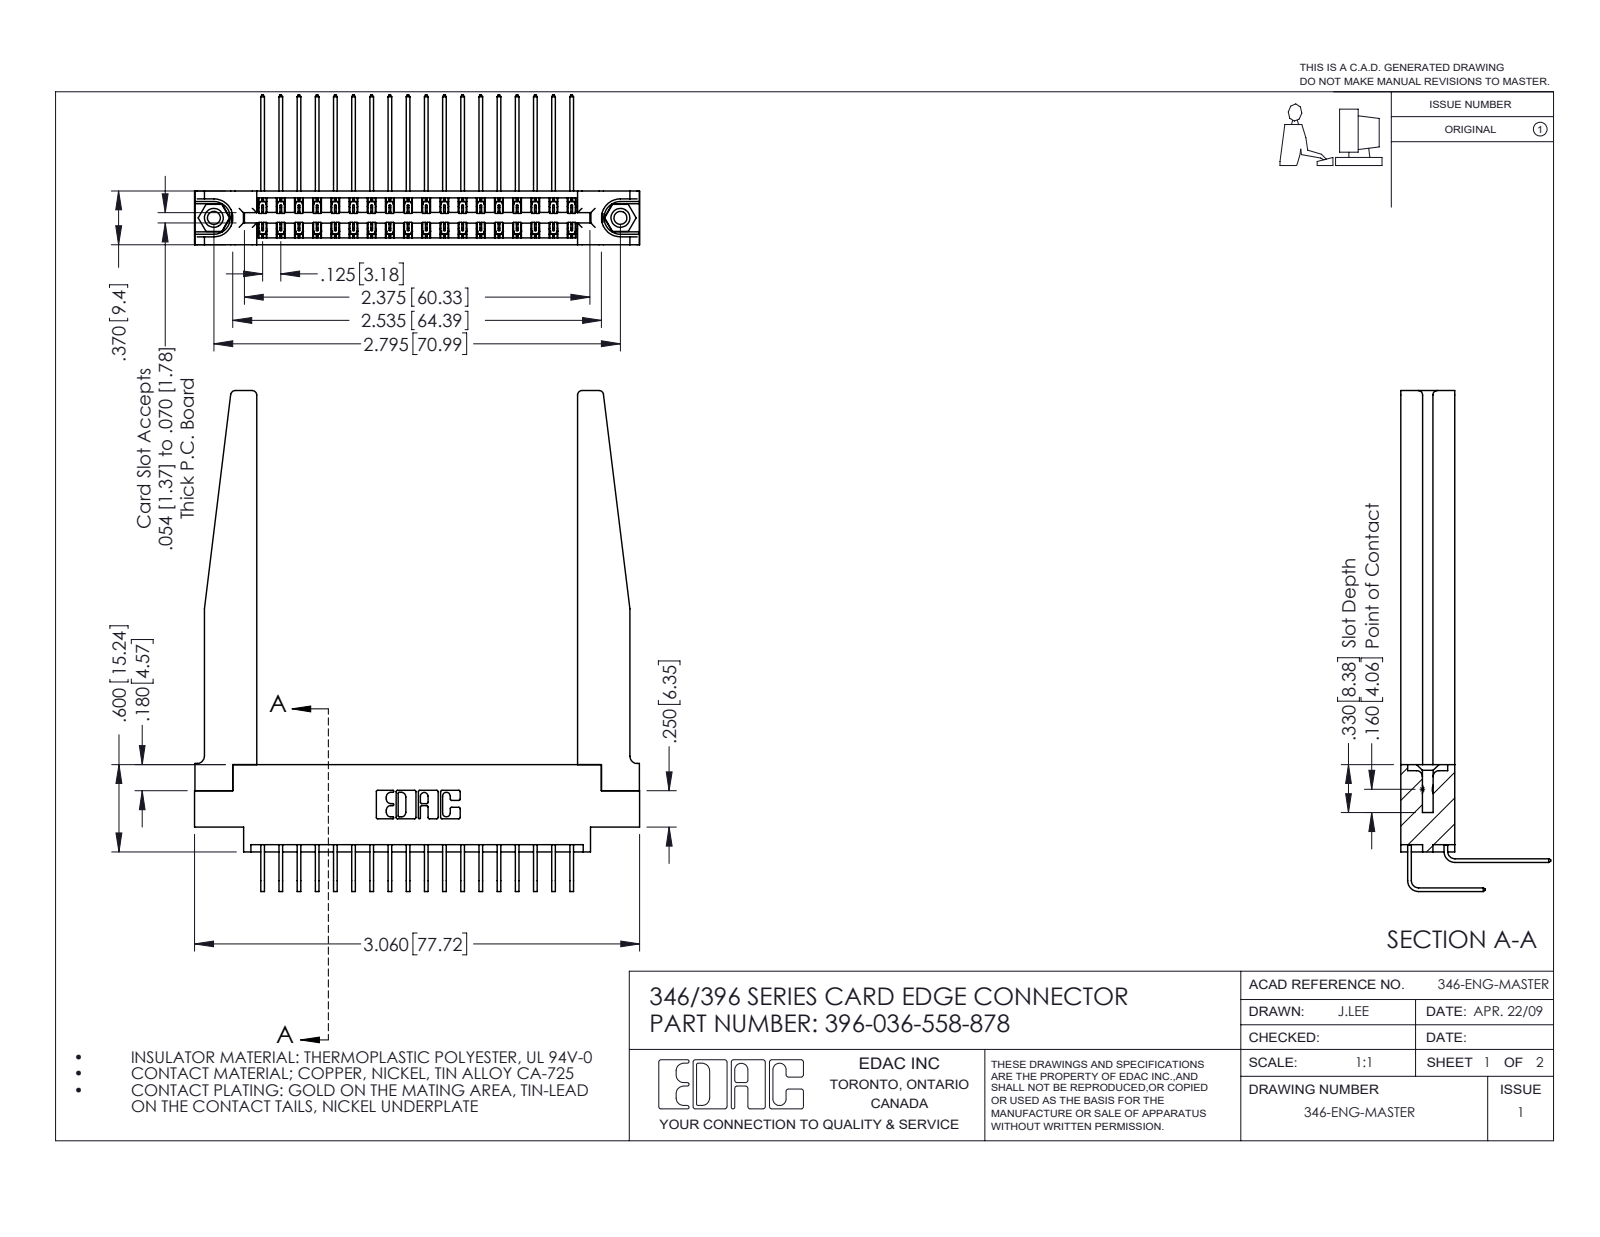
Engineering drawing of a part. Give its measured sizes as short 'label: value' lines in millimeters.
name: 346 Part_0.170 Offset - 0.156 Dia-TH; 345-250-001_345-250-001-102; 345-292-001_558 559 Tail - 1; 346-220-078_345-220-078 (+2 more)
written by: SolidWorks 2016 (CONFIG_CONTROL_DESIGN)
unit: mm
bodies: 41 solids, 2304 faces (1554 planar, 698 cylindrical, 52 other)
size: 87.5 × 77.7 × 26.2
volume: 14 400 mm³; area: 17 570 mm²
holes: 2× ⌀2.3, 2× ⌀3.2, 2× ⌀4, 1× ⌀1.6
bosses: 2× ⌀3.9
rounds: 54× R0.2, 22× R0.3, 8× R0.8, 6× R0.2, 6× R0.8, 4× R1.3, 3× R0.7, 2× R0.4
face distances: 9.4, 8.2, 1.2, 1.8, 3.8, 3.8, 0.6, 6.4, 7.6, 5.6
hole spacings: 6.2, 65.7, 71
